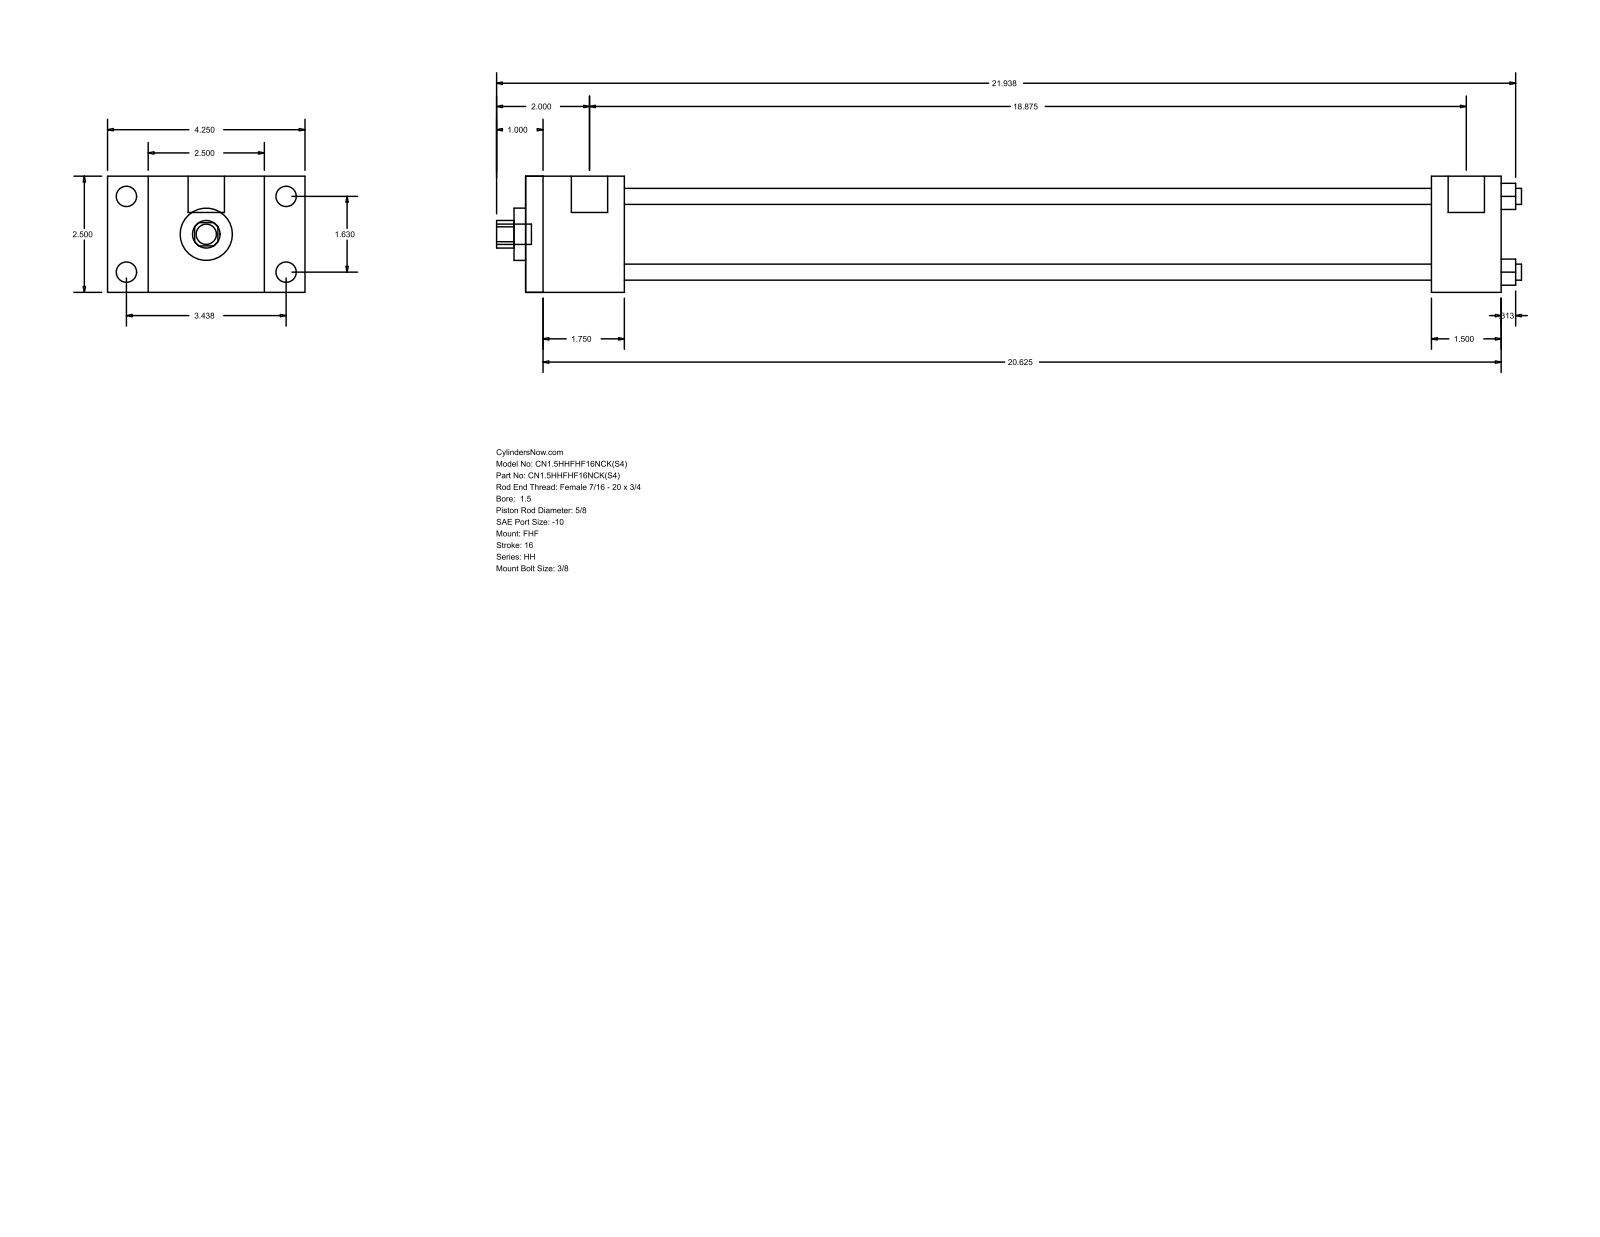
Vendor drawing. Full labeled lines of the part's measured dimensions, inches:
Part name (STEP PRODUCT): HH_FHF__0150_0.625
STEP written by: GSSL Pune (CONFIG_CONTROL_DESIGN)
Units: inches
Bodies: 0 solids, 88 faces (60 planar, 28 cylindrical, 0 other)
Overall size (bounding box): 22.063 × 4.25 × 2.5
Round holes (diameter × count): ⌀0.345 ×4, ⌀0.625 ×1, ⌀1.125 ×1, ⌀1.75 ×1
Round bosses / shafts (diameter × count): ⌀0.438 ×4, ⌀0.219 ×4, ⌀0.781 ×2, ⌀0.437 ×1
Partial cylindrical surfaces — rounded edges, fillets, slot ends (radius × count): R0.297 ×1
Main face-to-face distances: 2.5, 0.875, 3.375, 2.125, 4.25, 21, 18.875, 19.5, 17.375, 1.5
Hole centre spacings: 1.152, 1.63, 2.305
